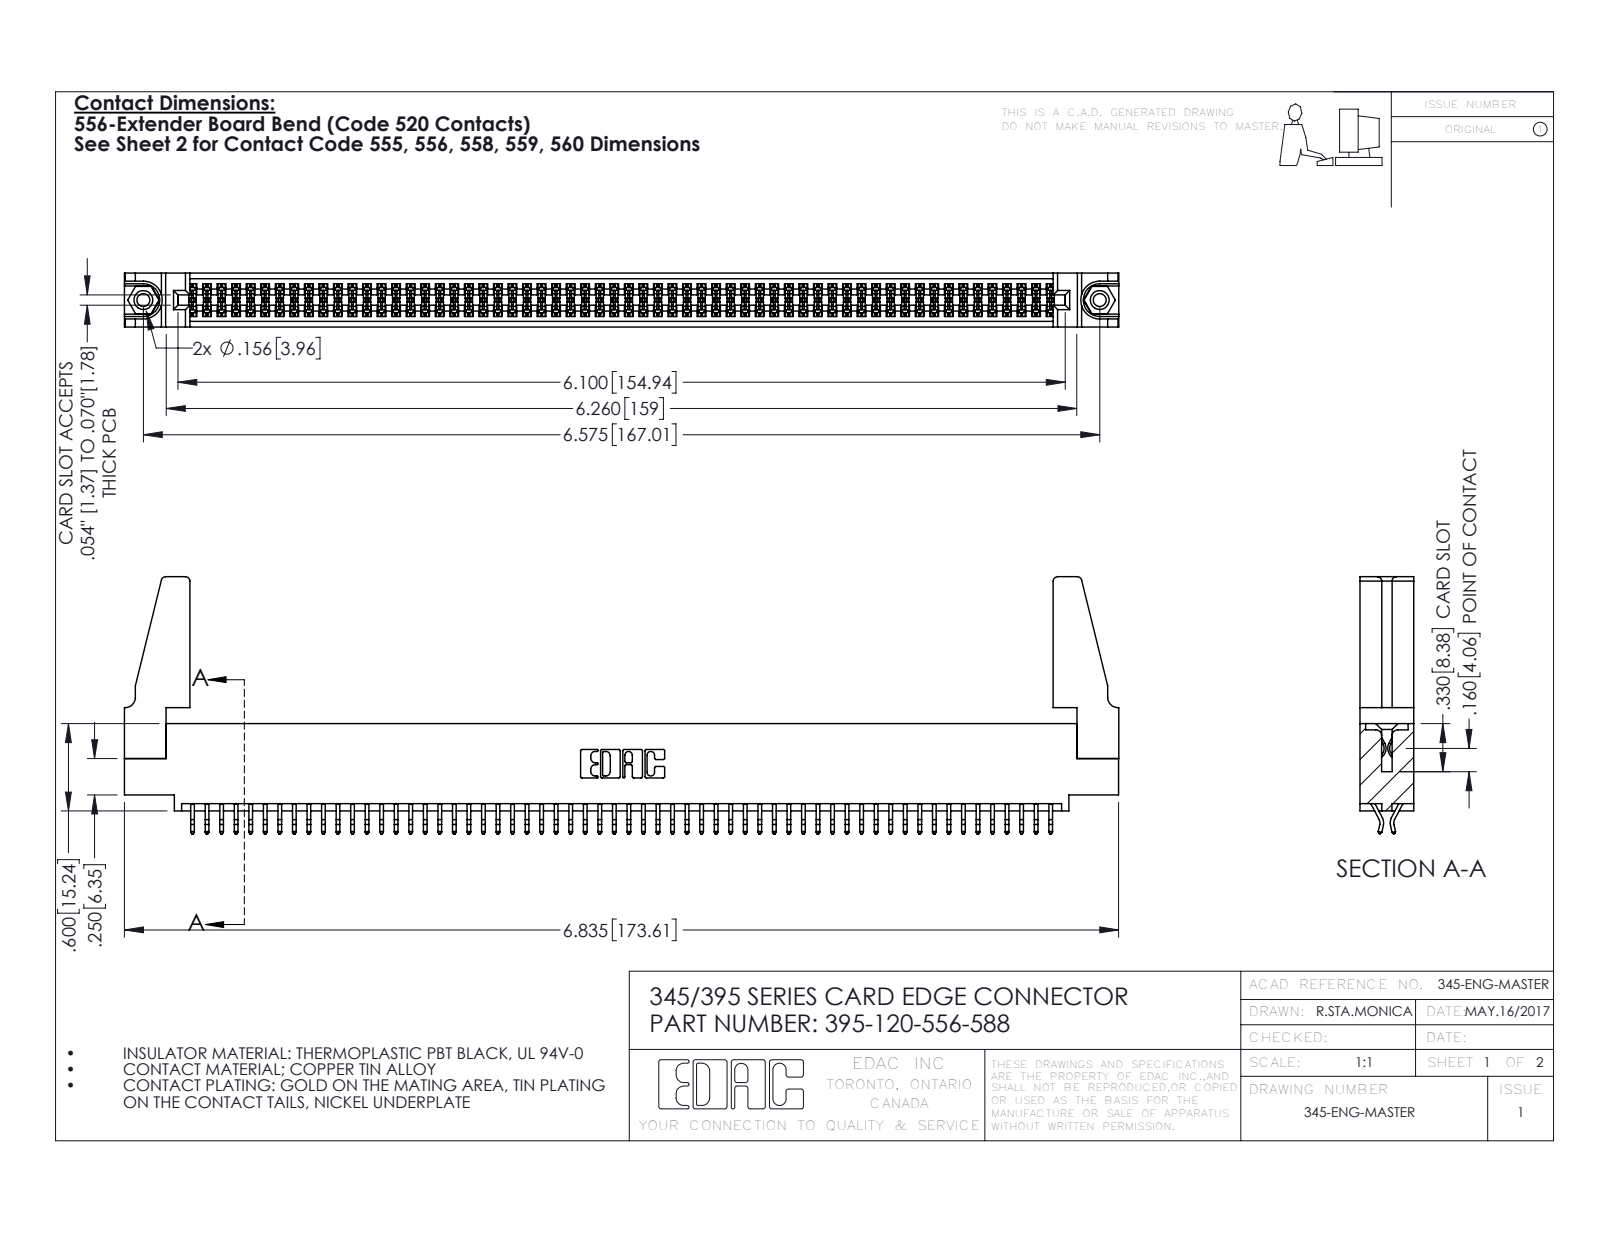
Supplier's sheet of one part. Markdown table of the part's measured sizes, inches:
| quantity | value |
| --- | --- |
| part name | 345 Part_0.110 Offset - 0.156 Dia-TH; 345-250-001_345-250-001-102; 345-220-078_345-220-088; 395-120-556-588 (+1 more) |
| STEP written by | SolidWorks 2016 (CONFIG_CONTROL_DESIGN) |
| units | inches |
| bodies | 125 solids, 6974 faces (4596 planar, 2362 cylindrical, 16 other) |
| overall size | 6.836 × 1.767 × 0.37 |
| volume | 1.233 in³ |
| surface area | 44.21 in² |
| round holes (diameter × count) | 0.089 × 2, 0.125 × 2, 0.156 × 2, 0.064 × 1 |
| round bosses / shafts (diameter × count) | 0.155 × 2 |
| partial cylindrical surfaces (radius × count) | 0.006 × 180, 0.01 × 22, 0.03 × 8, 0.007 × 6, 0.031 × 6, 0.026 × 3, 0.01 × 2, 0.014 × 2 |
| main face-to-face distances | 0.072, 0.298, 0.37, 0.025, 0.2, 0.098, 0.272, 0.225, 0.175, 0.149 |
| hole center spacings | 0.27, 6.339, 6.575 |
